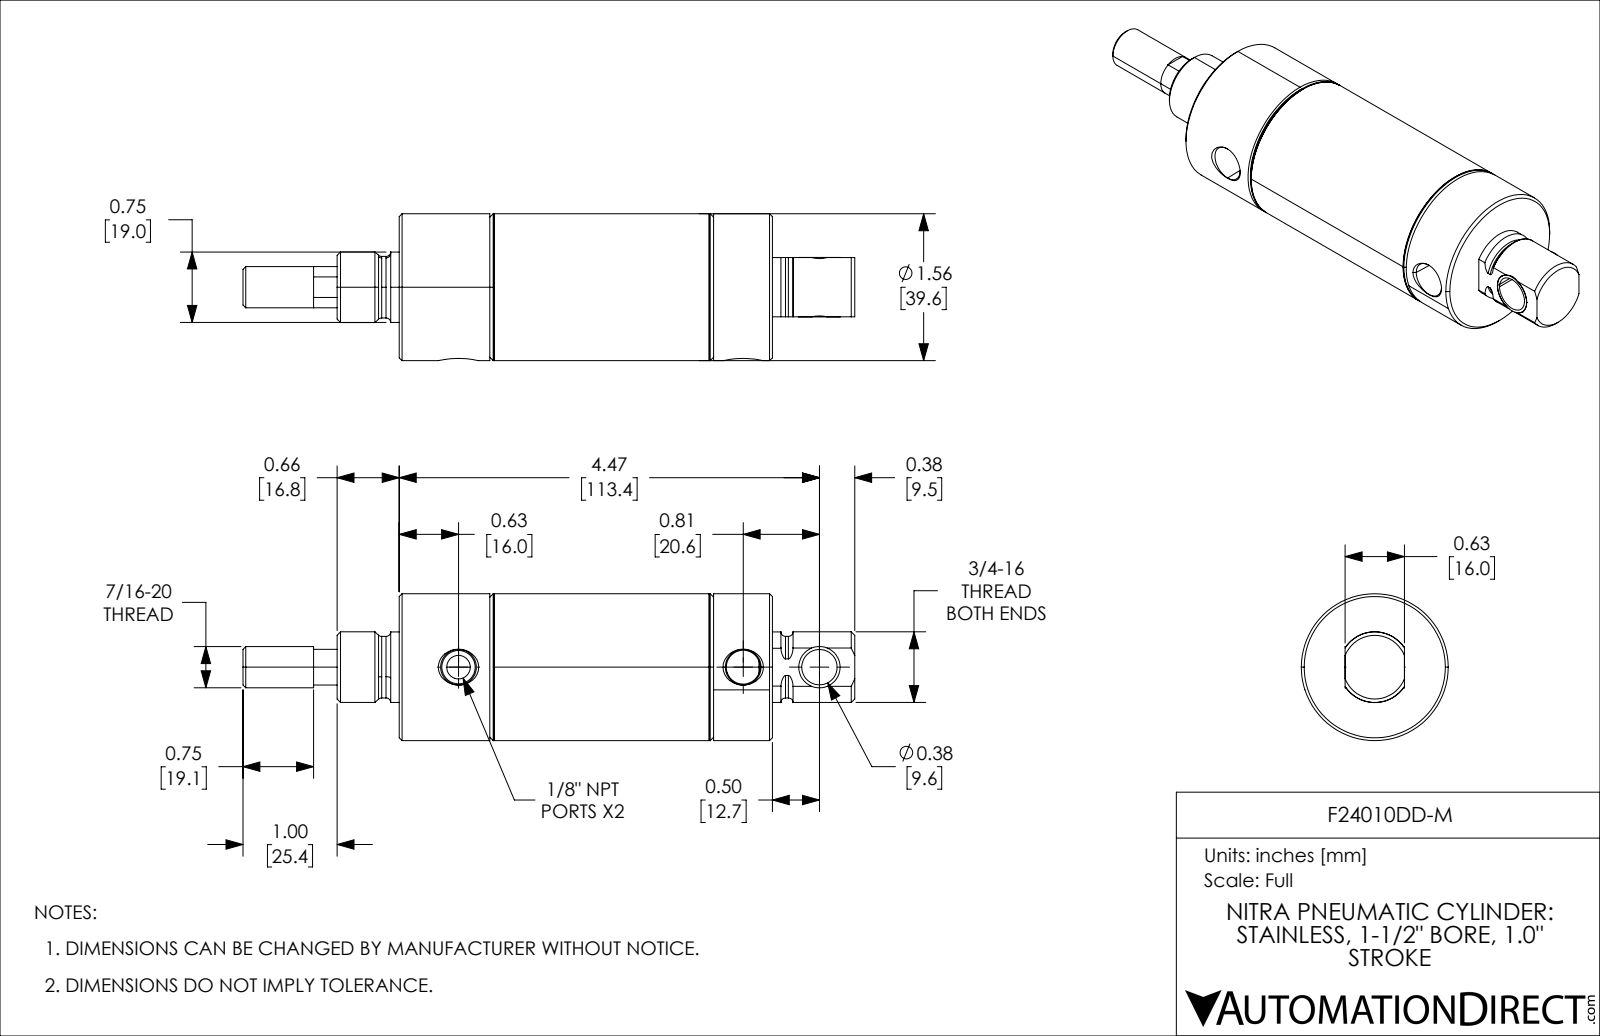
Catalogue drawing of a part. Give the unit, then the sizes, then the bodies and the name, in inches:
Units: inches
Overall size (bounding box): 6.5 × 1.56 × 1.56
Round holes (diameter × count): ⌀0.25 ×1, ⌀0.36 ×1, ⌀0.376 ×1, ⌀0.439 ×1, ⌀0.462 ×1, ⌀0.532 ×1, ⌀1.062 ×1, ⌀1.431 ×1
Round bosses / shafts (diameter × count): ⌀1.56 ×1, ⌀1.511 ×1, ⌀0.75 ×1, ⌀0.748 ×1, ⌀0.654 ×1, ⌀0.654 ×1, ⌀0.438 ×1, ⌀0.437 ×1
Main face-to-face distances: 0.875, 1.75, 1, 1.875, 2.75, 0.875, 1.215, 2.215, 3.09, 3.965
Hole centre spacings: 0.81, 3.025, 3.835
Volume: 6.102 in³ · Surface area: 66.22 in²
Bodies: 5 solids, 157 faces (35 planar, 58 cylindrical, 64 other)
Part name (STEP PRODUCT): F24010DD-M_7; F24010DD-M_5; F24010DD-M_9; F24010DD-M (+2 more)
STEP written by: SolidWorks 2021 (CONFIG_CONTROL_DESIGN)
